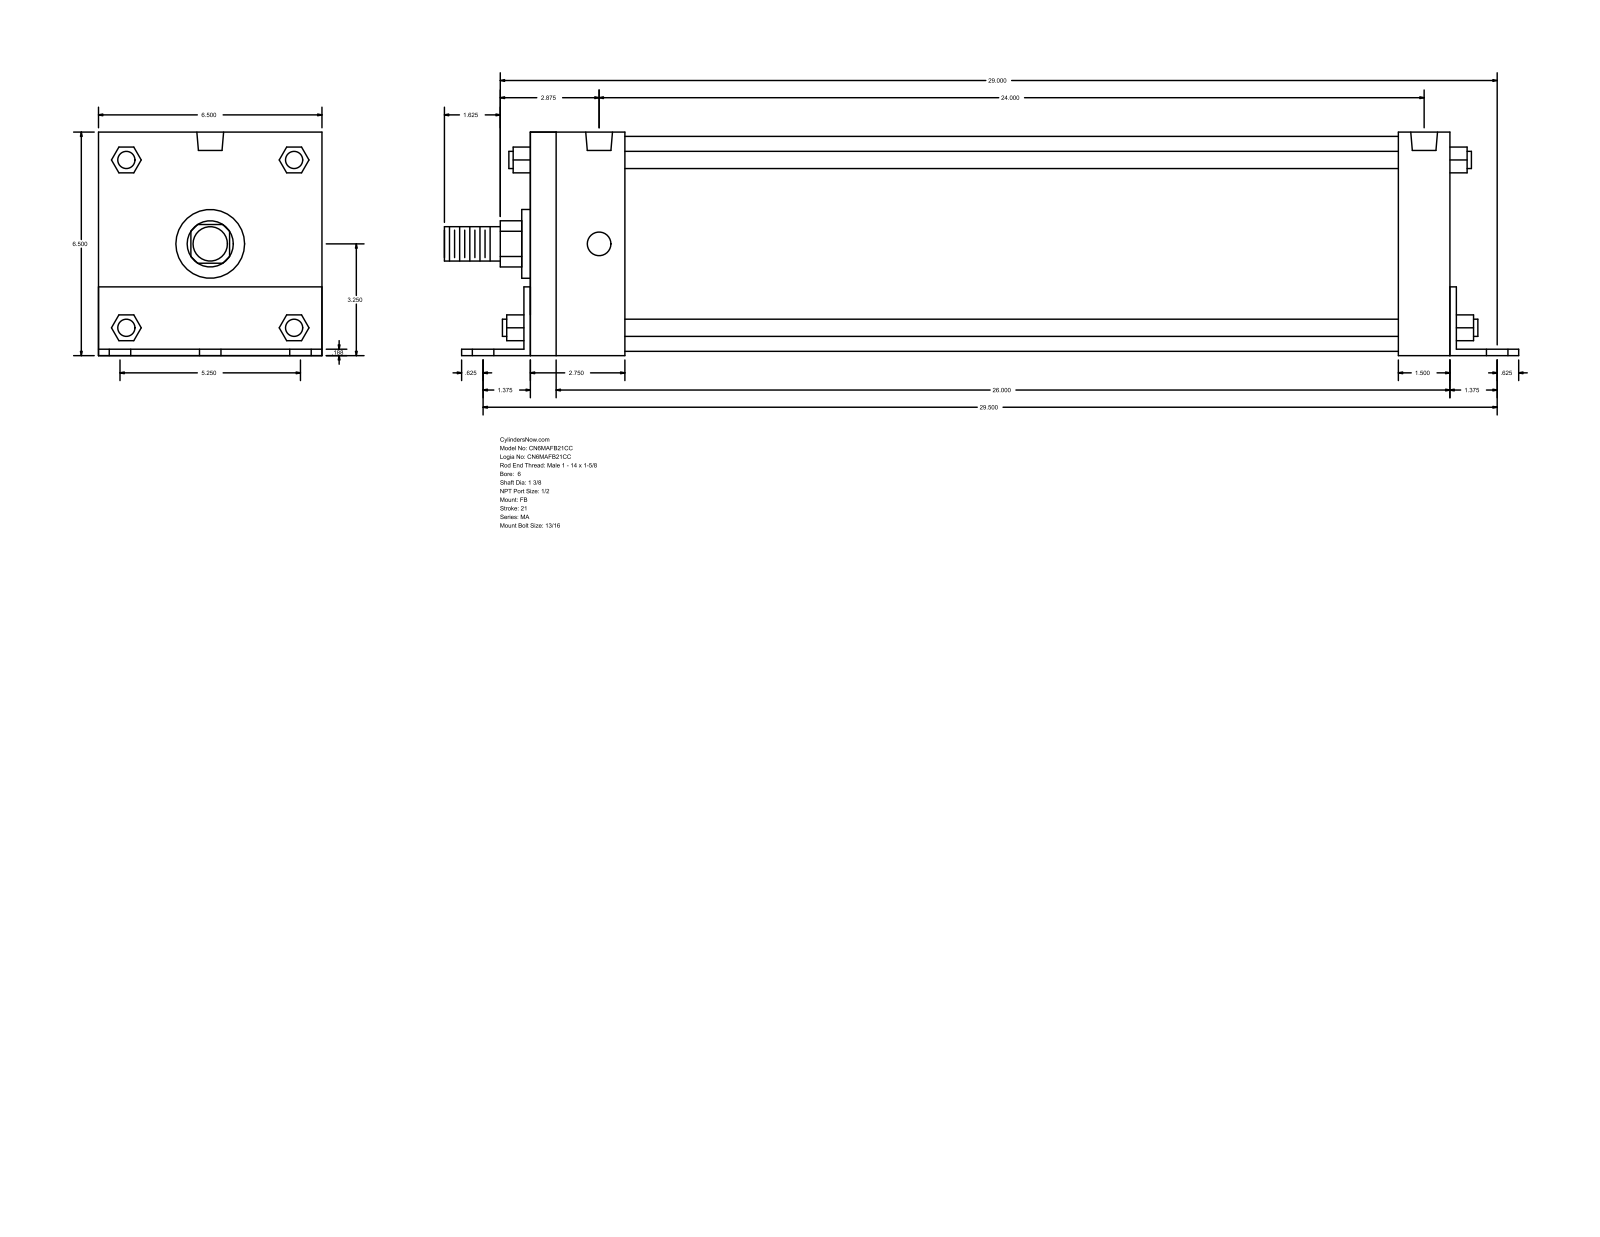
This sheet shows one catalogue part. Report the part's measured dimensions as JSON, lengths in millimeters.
{"part_name": "MA_FB__0600_1.375", "step_written_by": "GSSL Pune (CONFIG_CONTROL_DESIGN)", "units": "millimeters", "bodies": {"solids": 0, "faces": 140, "planar": 105, "cylindrical": 35, "other": 0}, "overall_size": [790.58, 165.15, 165.1], "round_holes": [[20.64, 6], [17.46, 4], [19.77, 2]], "round_bosses_or_shafts": [[12.7, 4], [158.75, 1], [50.8, 1], [34.92, 1], [25.4, 1]], "partial_cylinders_radius": [[17.06, 1], [32.05, 1]], "face_to_face_distances": [165.1, 4.76, 676.27, 165.15, 4.71, 160.39, 4.77, 38.1, 42.86, 685.8], "hole_center_spacings": [66.67, 749.09, 746.12, 83.82, 85.78, 108.6, 133.34, 606.42]}
